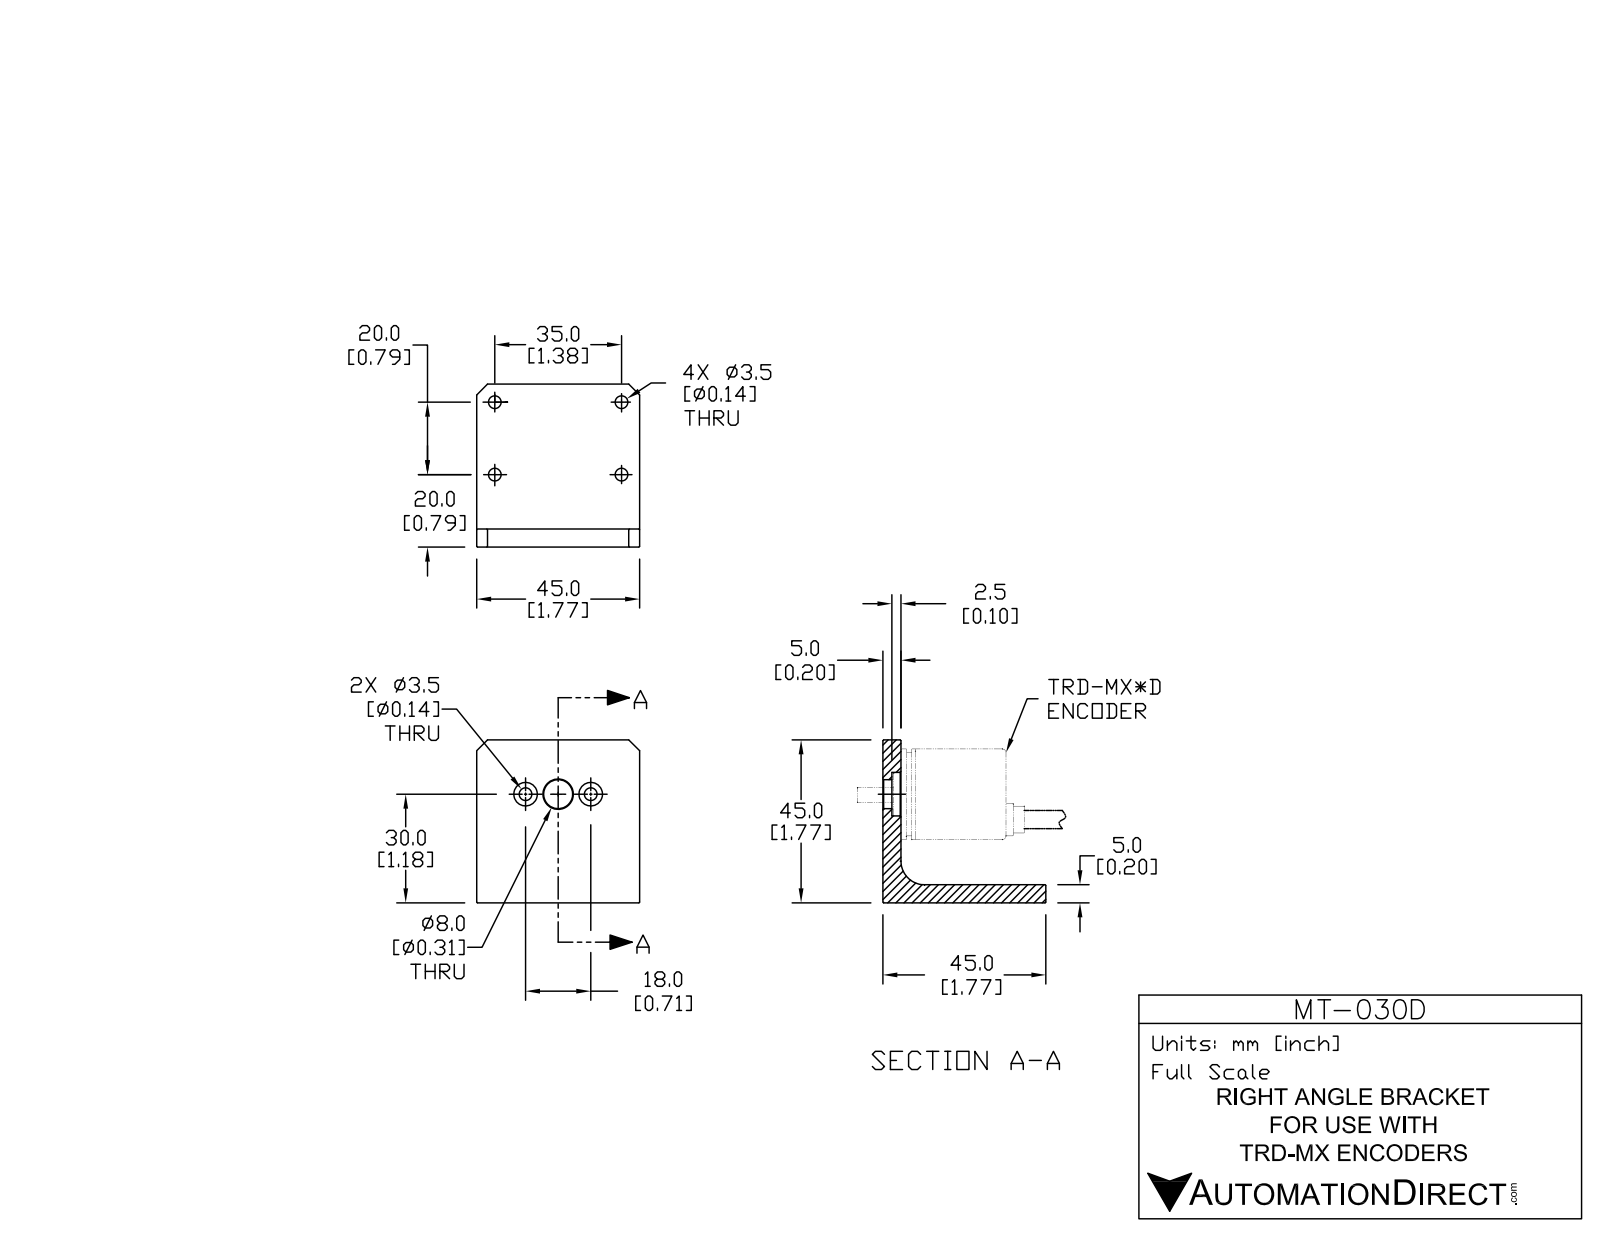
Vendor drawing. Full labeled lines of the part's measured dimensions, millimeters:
Part name (STEP PRODUCT): MT-030D
STEP written by: SolidWorks 2016 (AUTOMOTIVE_DESIGN)
Units: millimetres
Bodies: 1 solid, 56 faces (29 planar, 19 cylindrical, 8 other)
Overall size (bounding box): 45 × 45 × 45
Volume: 18 329 mm³ · Surface area: 8 996 mm²
Round holes (diameter × count): ⌀3.5 ×6, ⌀8 ×1, ⌀12.1 ×1, ⌀28.5 ×1
Partial cylindrical surfaces — rounded edges, fillets, slot ends (radius × count): R5 ×1
Main face-to-face distances: 5, 45, 0.4, 4.6, 40, 40.4, 2.5, 42.5, 2.1, 61.37
Hole centre spacings: 9, 20, 35, 40.31, 18
